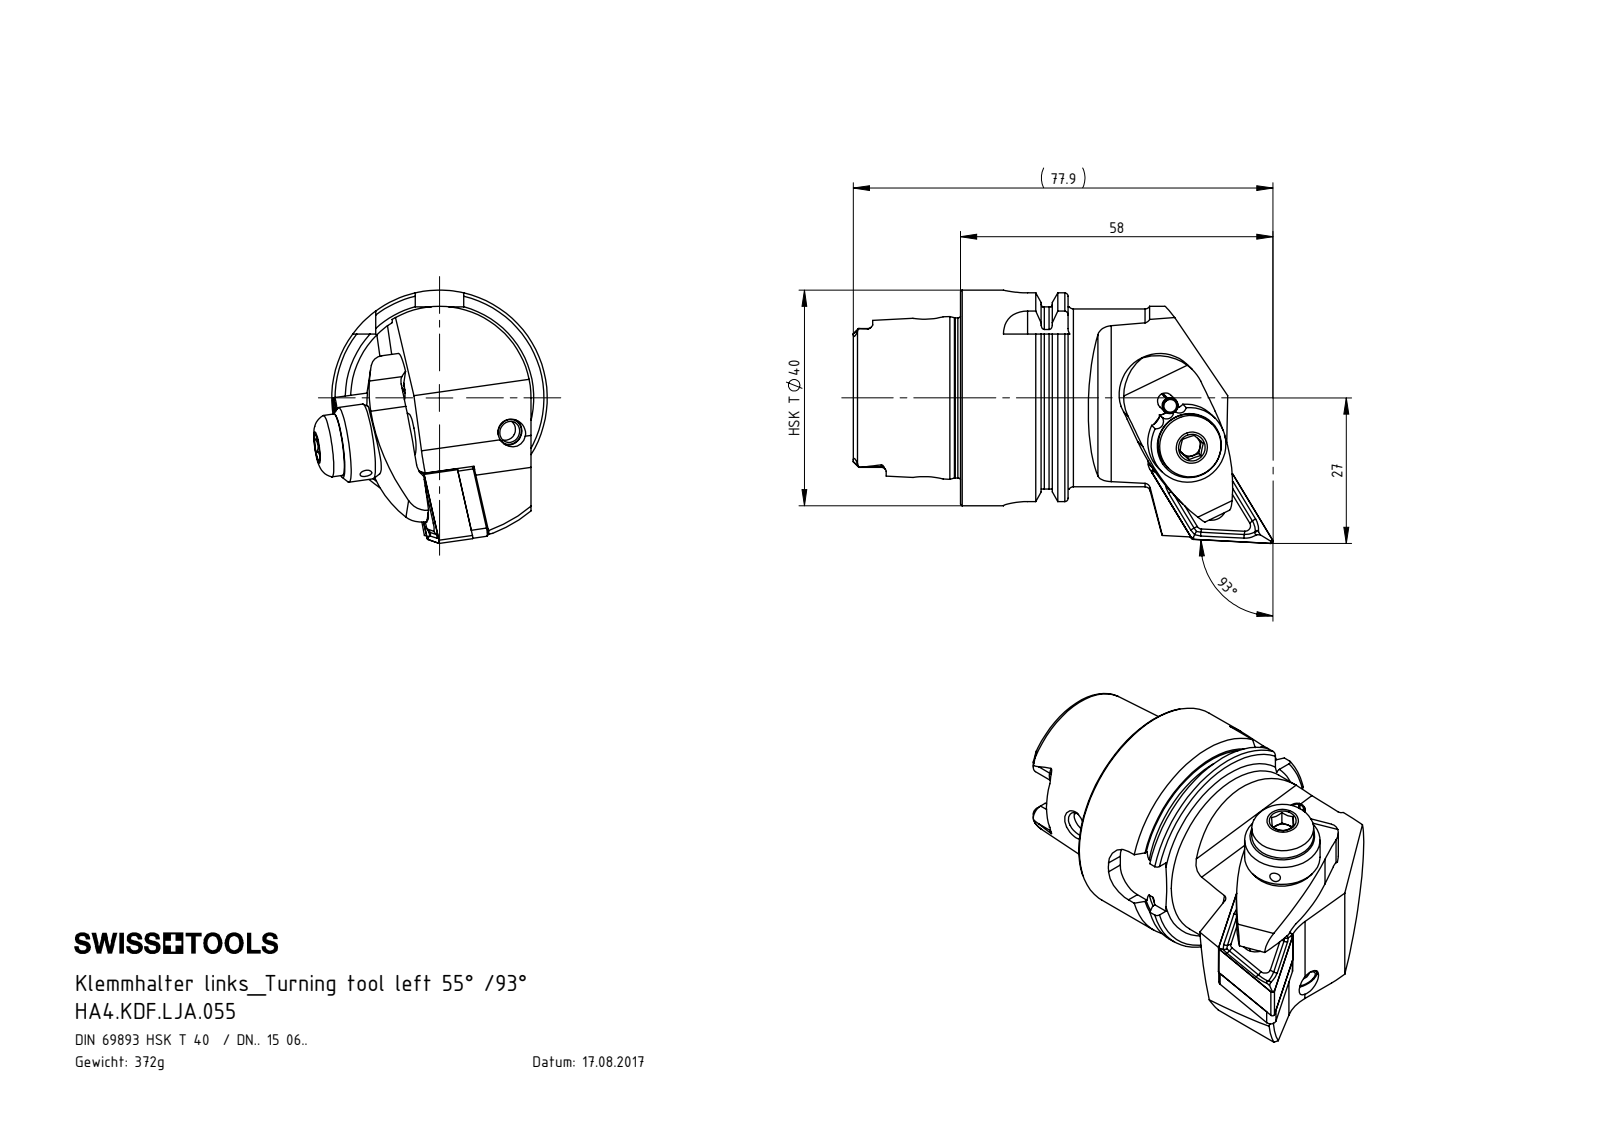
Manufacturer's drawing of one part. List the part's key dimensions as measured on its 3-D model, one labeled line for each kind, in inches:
Part name (STEP PRODUCT): WCC-ER3.102.024_C; WCC-ER5.102.005_A; WCC-ER2.001.010_A; HA4.KDF.LJA.055 (+7 more)
STEP written by: SolidWorks 2017 (AUTOMOTIVE_DESIGN)
Units: inches
Bodies: 11 solids, 469 faces (125 planar, 154 cylindrical, 190 other)
Overall size (bounding box): 3.067 × 1.85 × 1.706
Volume: 2.949 in³ · Surface area: 29.81 in²
Round holes (diameter × count): ⌀0.079 ×3, ⌀0.165 ×2, ⌀0.197 ×2, ⌀0.276 ×2, ⌀0.094 ×1, ⌀0.118 ×1, ⌀0.157 ×1, ⌀0.181 ×1, ⌀0.203 ×1, ⌀0.244 ×1, ⌀0.252 ×1, ⌀0.335 ×1
Round bosses / shafts (diameter × count): ⌀0.197 ×2, ⌀0.118 ×2, ⌀1.575 ×1, ⌀1.368 ×1, ⌀1.299 ×1, ⌀1.17 ×1, ⌀0.551 ×1, ⌀0.453 ×1
Partial cylindrical surfaces — rounded edges, fillets, slot ends (radius × count): R0.015 ×6, R0.035 ×6, R0.016 ×4, R0.027 ×4, R0.039 ×4, R0.074 ×4, R0.177 ×4, R0.059 ×3
Main face-to-face distances: 0.237, 0.362, 0.125, 0.313, 0.015, 0.414, 0.289, 0.052, 0.472, 0.785
Hole centre spacings: 0.323, 0.583, 0.906, 0.591, 0.315, 0.315, 0.323, 0.582
